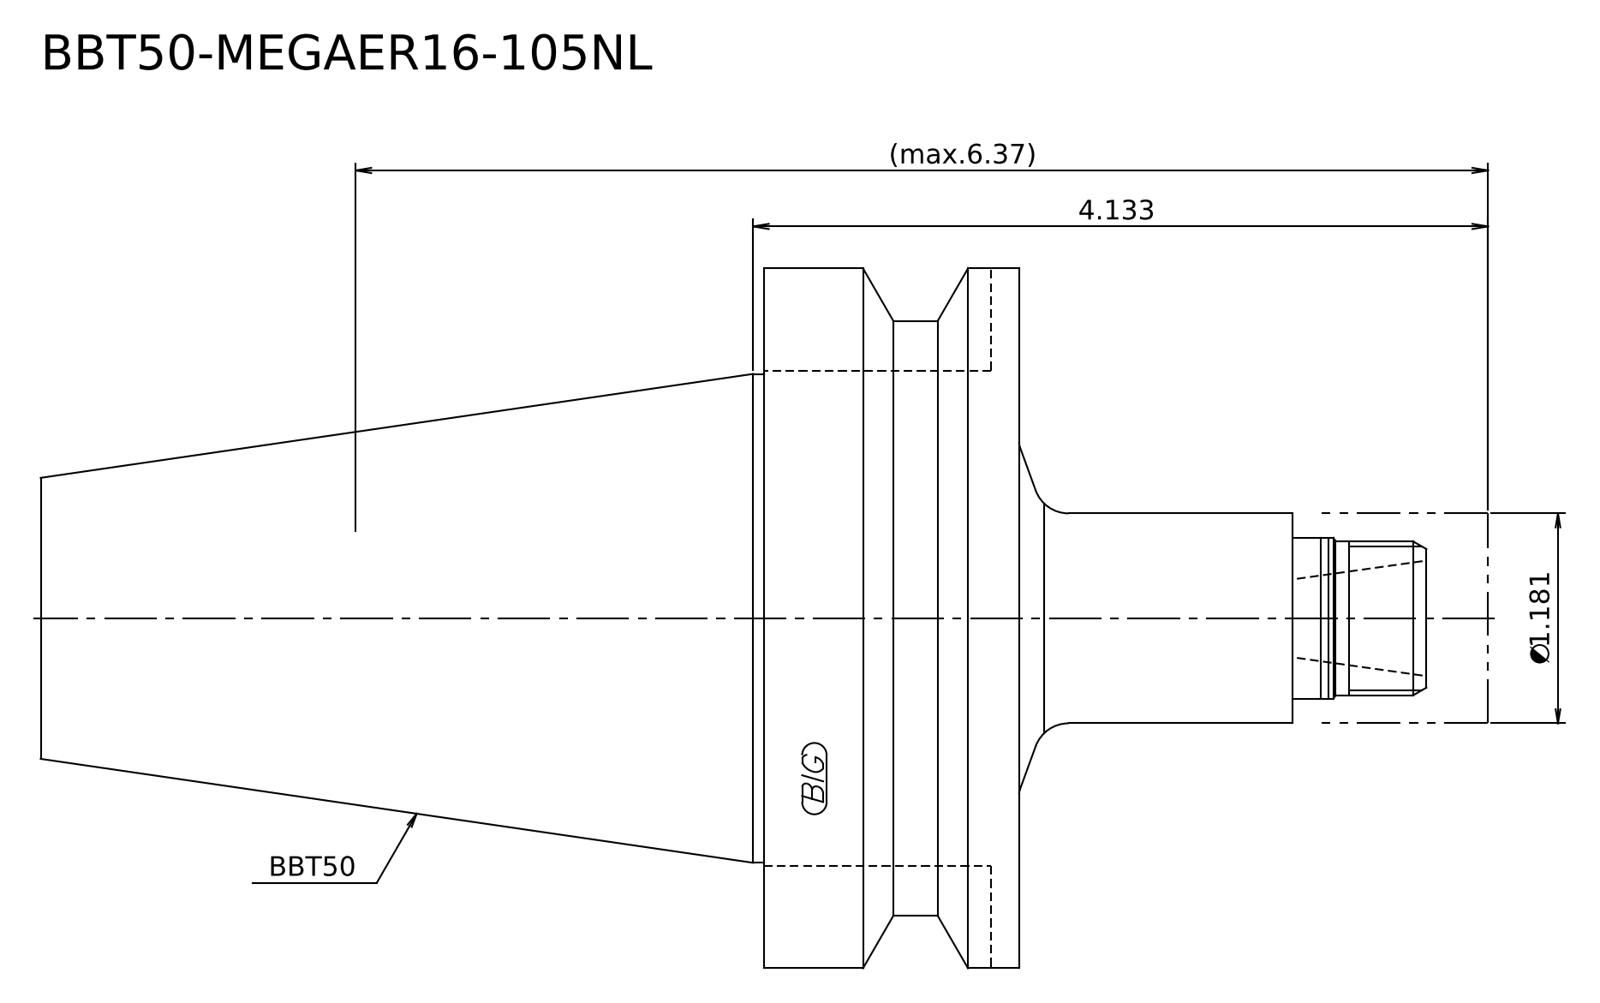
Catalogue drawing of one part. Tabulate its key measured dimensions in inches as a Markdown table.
| quantity | value |
| --- | --- |
| STEP written by | Kubotek KeyCreator 2011 V10.0.2 (22737) (automotive_design) |
| units | inches |
| bodies | 2 solids, 21 faces (7 planar, 8 cylindrical, 6 other) |
| overall size | 206.8 × 100 × 100 |
| volume | 573 527 in³ |
| surface area | 53 063 in² |
| round bosses / shafts (diameter × count) | 100 × 1, 85 × 1, 69.85 × 1, 30 × 1, 23 × 1, 22 × 1 |
| main face-to-face distances | 36.5, 139.8, 103.3, 42, 78.5, 181.8, 25, 67, 103.5, 206.8 |
